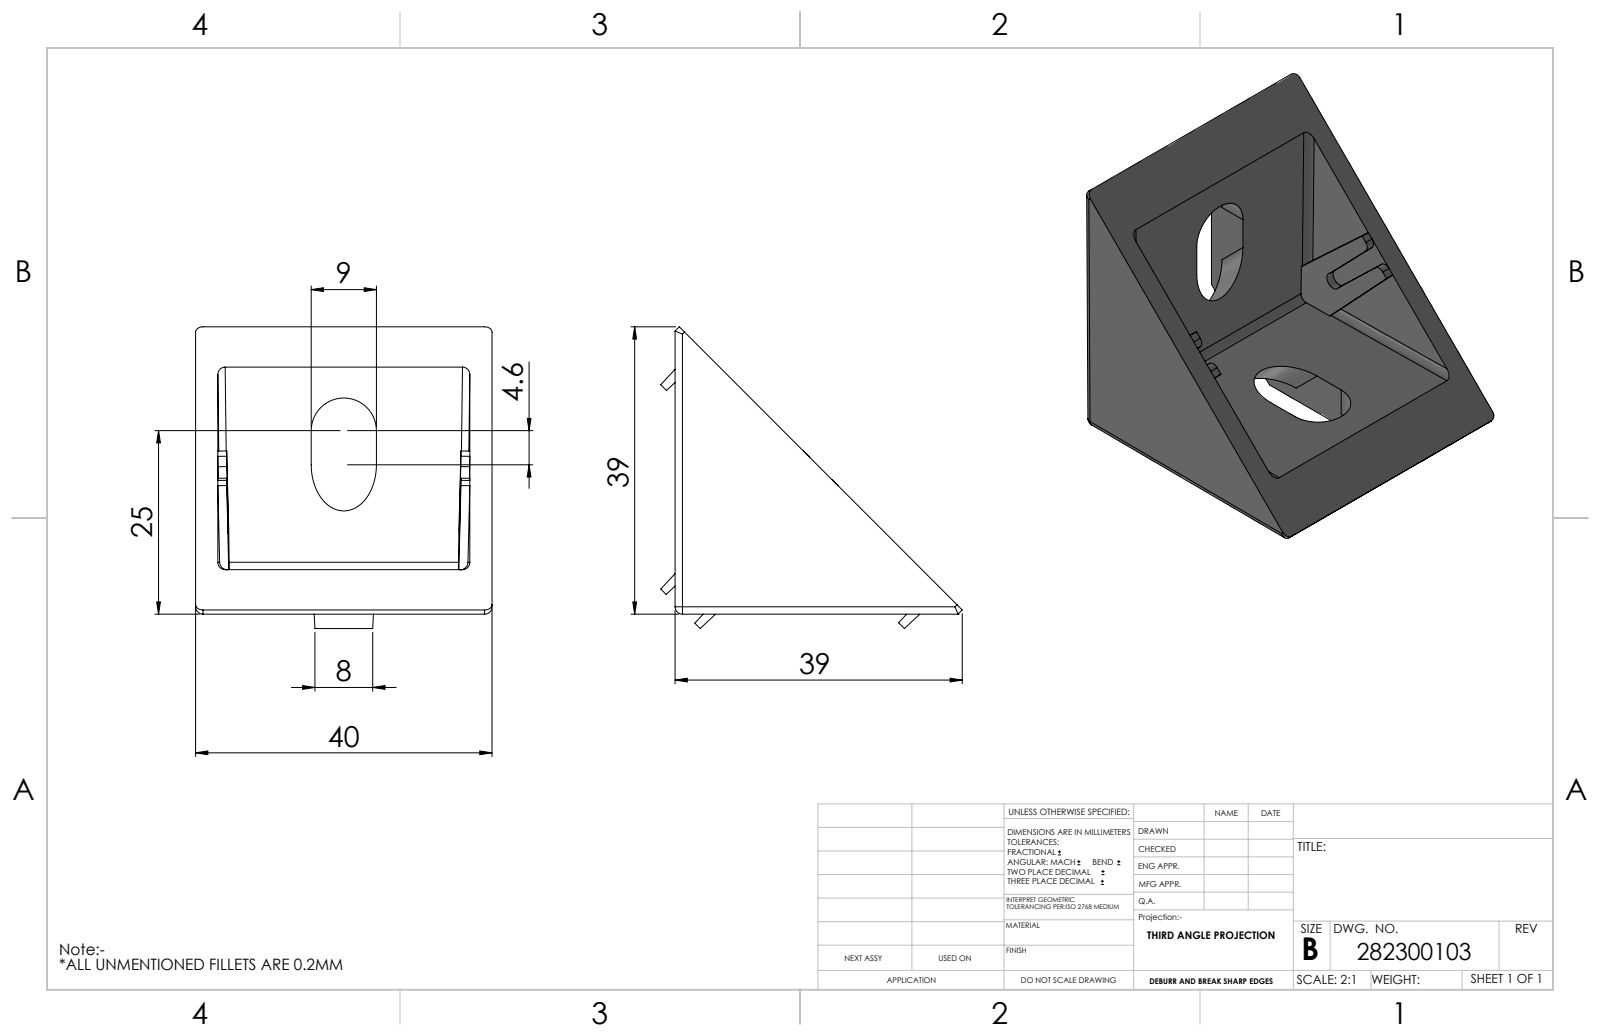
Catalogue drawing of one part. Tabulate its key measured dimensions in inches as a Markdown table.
| quantity | value |
| --- | --- |
| part name | 282300103 |
| STEP written by | SolidWorks 2014 (AUTOMOTIVE_DESIGN) |
| units | inches |
| bodies | 1 solid, 169 faces (112 planar, 53 cylindrical, 4 other) |
| overall size | 2.126 × 1.575 × 1.079 |
| volume | 0.807 in³ |
| surface area | 14.71 in² |
| round bosses / shafts (diameter × count) | 0.157 × 4 |
| partial cylindrical surfaces (radius × count) | 0.039 × 34, 0.173 × 4, 0.02 × 2, 0.046 × 2 |
| main face-to-face distances | 0.236, 0.118, 0.118, 1.023, 0.047, 0.079, 0.157, 0.039, 0.083, 0.429 |
